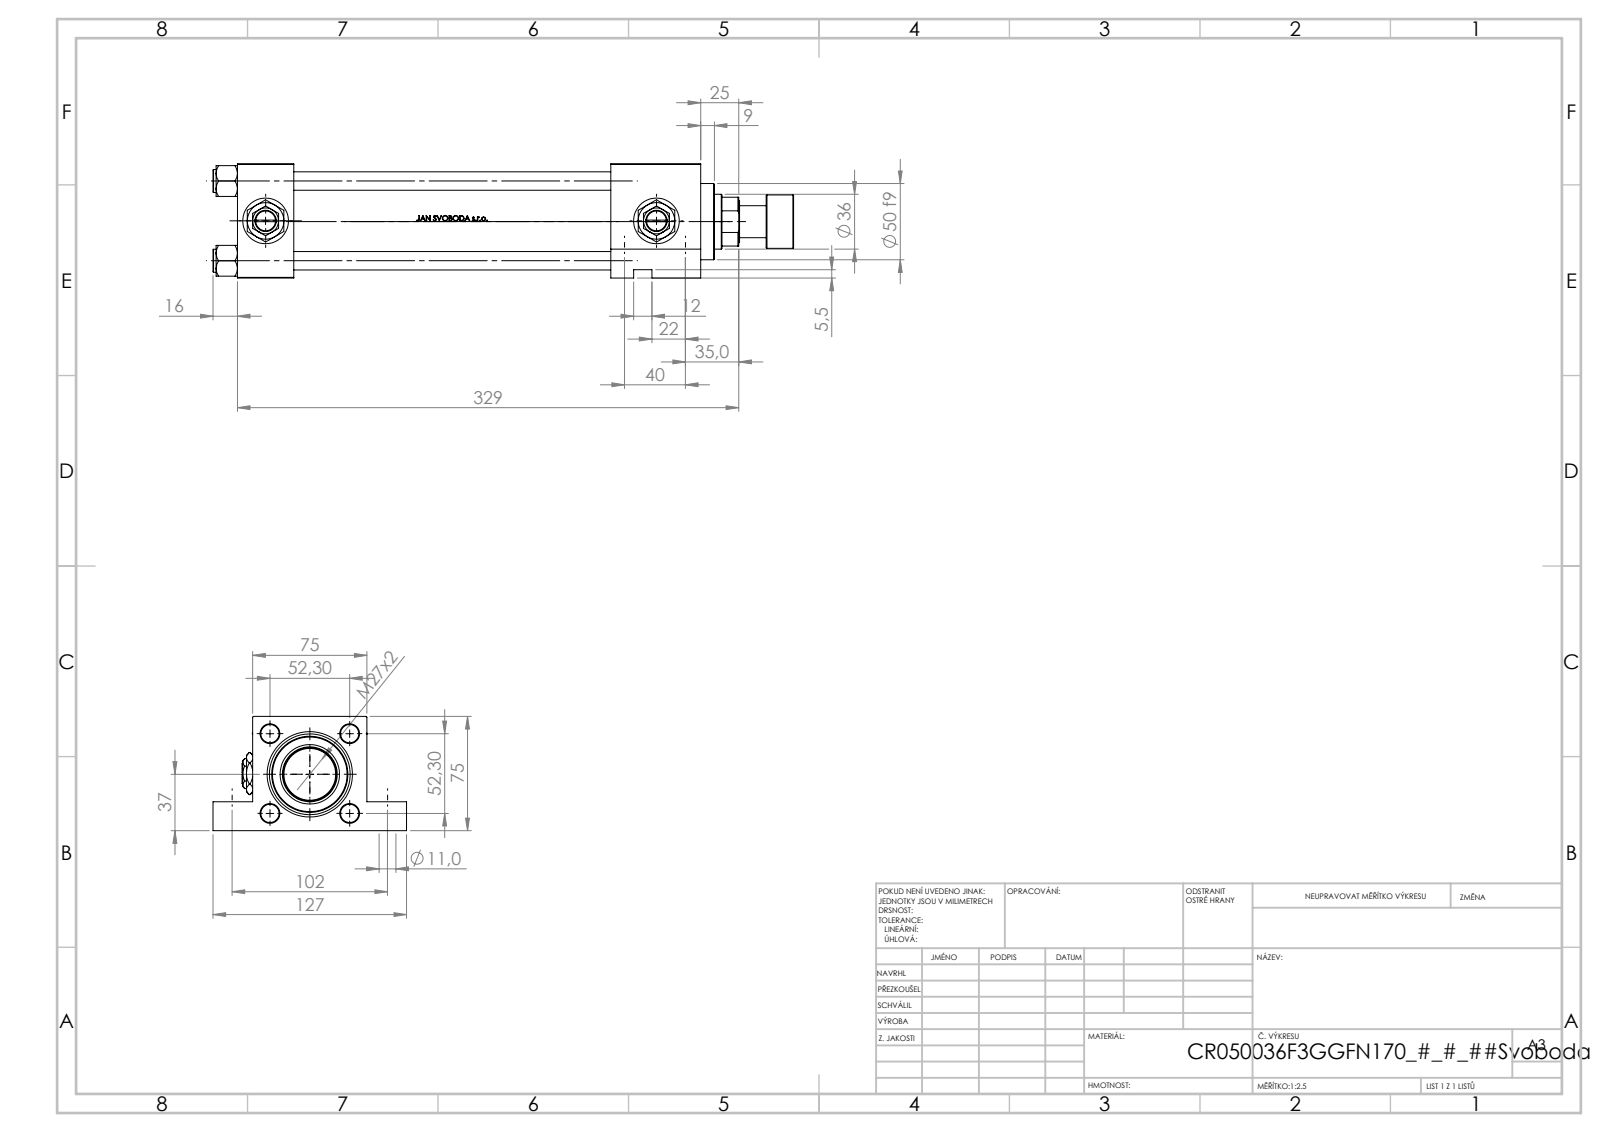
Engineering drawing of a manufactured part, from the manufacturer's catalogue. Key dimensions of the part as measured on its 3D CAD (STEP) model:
Part name (STEP PRODUCT): V215CR_VCP_F; V215_VC_A; V215CR_F_TYCINKA; NUT_M5_F (+3 more)
STEP written by: SolidWorks 2019 (CONFIG_CONTROL_DESIGN)
Units: millimetres
Bodies: 14 solids, 1216 faces (488 planar, 140 cylindrical, 588 other)
Overall size (bounding box): 381 × 127 × 75
Volume: 1 049 000 mm³ · Surface area: 264 076 mm²
Round holes (diameter × count): ⌀11 ×4, ⌀12 ×4, ⌀20.96 ×4, ⌀30 ×4, ⌀7 ×3, ⌀25.5 ×1, ⌀36 ×1, ⌀39 ×1, ⌀41 ×1, ⌀53 ×1
Round bosses / shafts (diameter × count): ⌀15 ×4, ⌀56 ×1, ⌀50 ×1, ⌀35 ×1, ⌀21 ×1
Main face-to-face distances: 75, 37, 245, 208, 59, 304, 267, 19, 56, 74.8
Hole centre spacings: 52.3, 36.63, 37.34, 40, 51.62, 60.21, 73.96, 102
